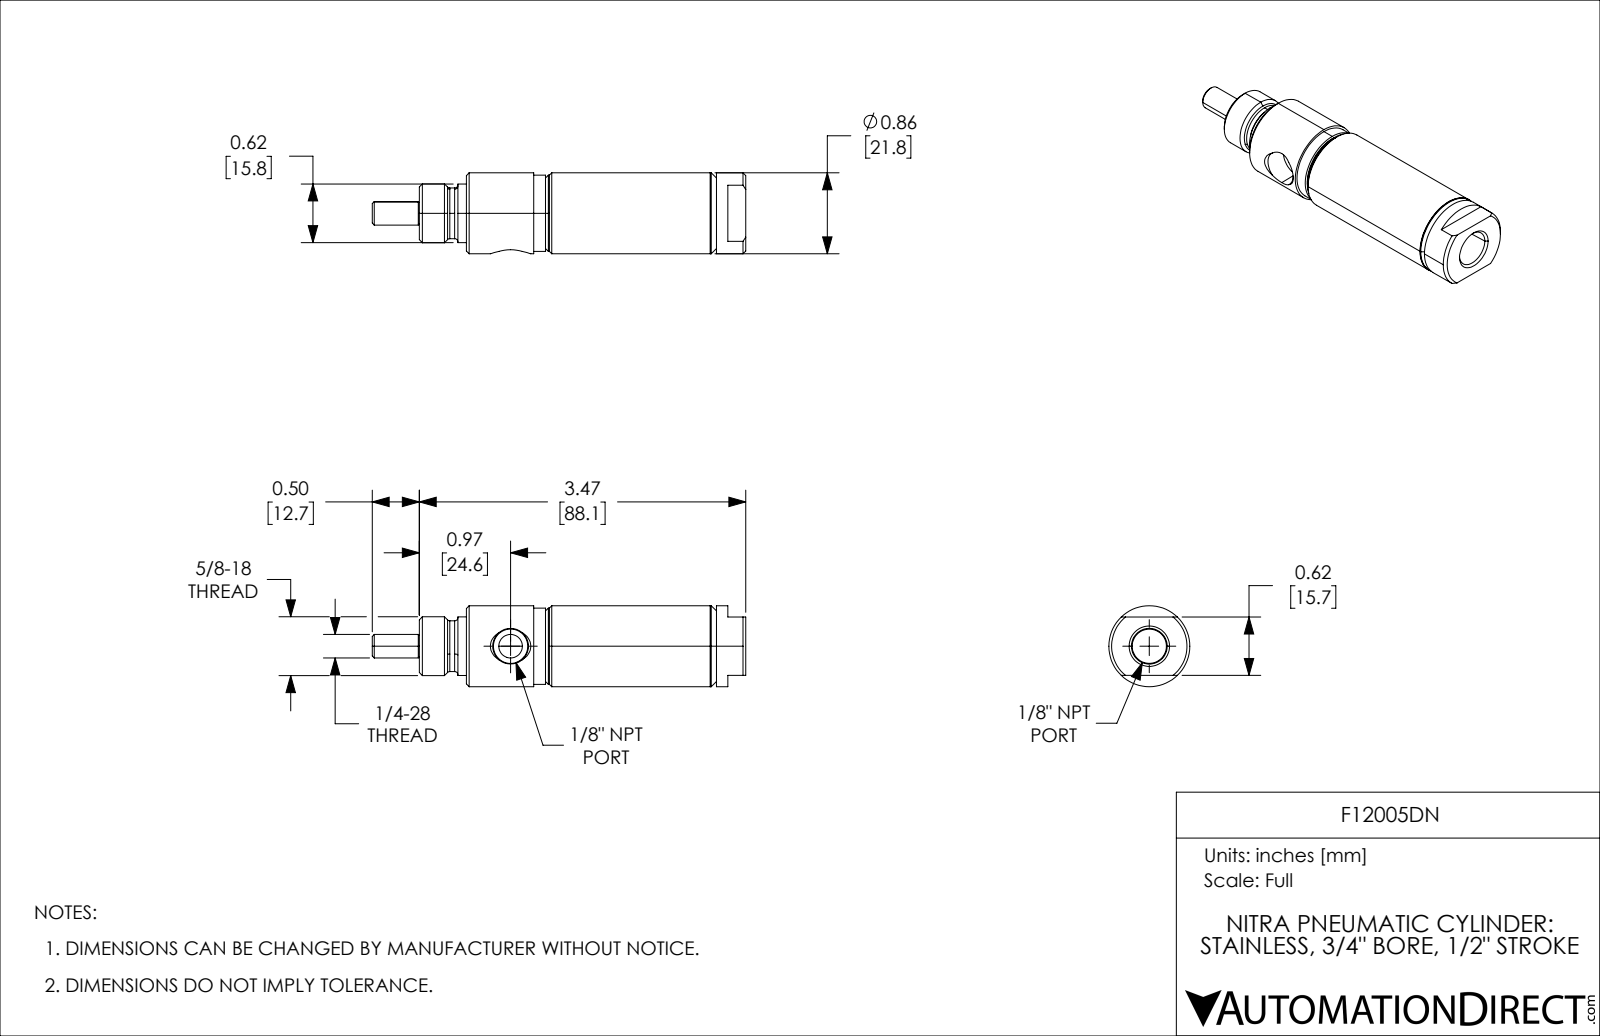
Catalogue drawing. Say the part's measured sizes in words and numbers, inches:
The part is named "F12005DN_5; F12005DN; F12005DN_3; F12005DN_7 (+1 more)". Its 3-D file was written by "SolidWorks 2021 (CONFIG_CONTROL_DESIGN)". It is 4 solids with 124 faces: 22 planar, 46 cylindrical and 56 other. Overall it measures 3.969 by 0.86 by 0.86 inches. Its volume is 1.523 cubic inches and its surface area 24.52 square inches. Round holes: 1 of diameter 0.25, 1 of diameter 0.274, 1 of diameter 0.5, 1 of diameter 0.702. Round bosses or shafts: 1 of diameter 0.86, 1 of diameter 0.81, 1 of diameter 0.762, 1 of diameter 0.625, 1 of diameter 0.622, 1 of diameter 0.539, 1 of diameter 0.25, 1 of diameter 0.23. The main face-to-face distances are 0.5, 0.844, 1.594, 1.344, 1.875, 1.375, 0.531, 2.094, 1.094, 2.438.
